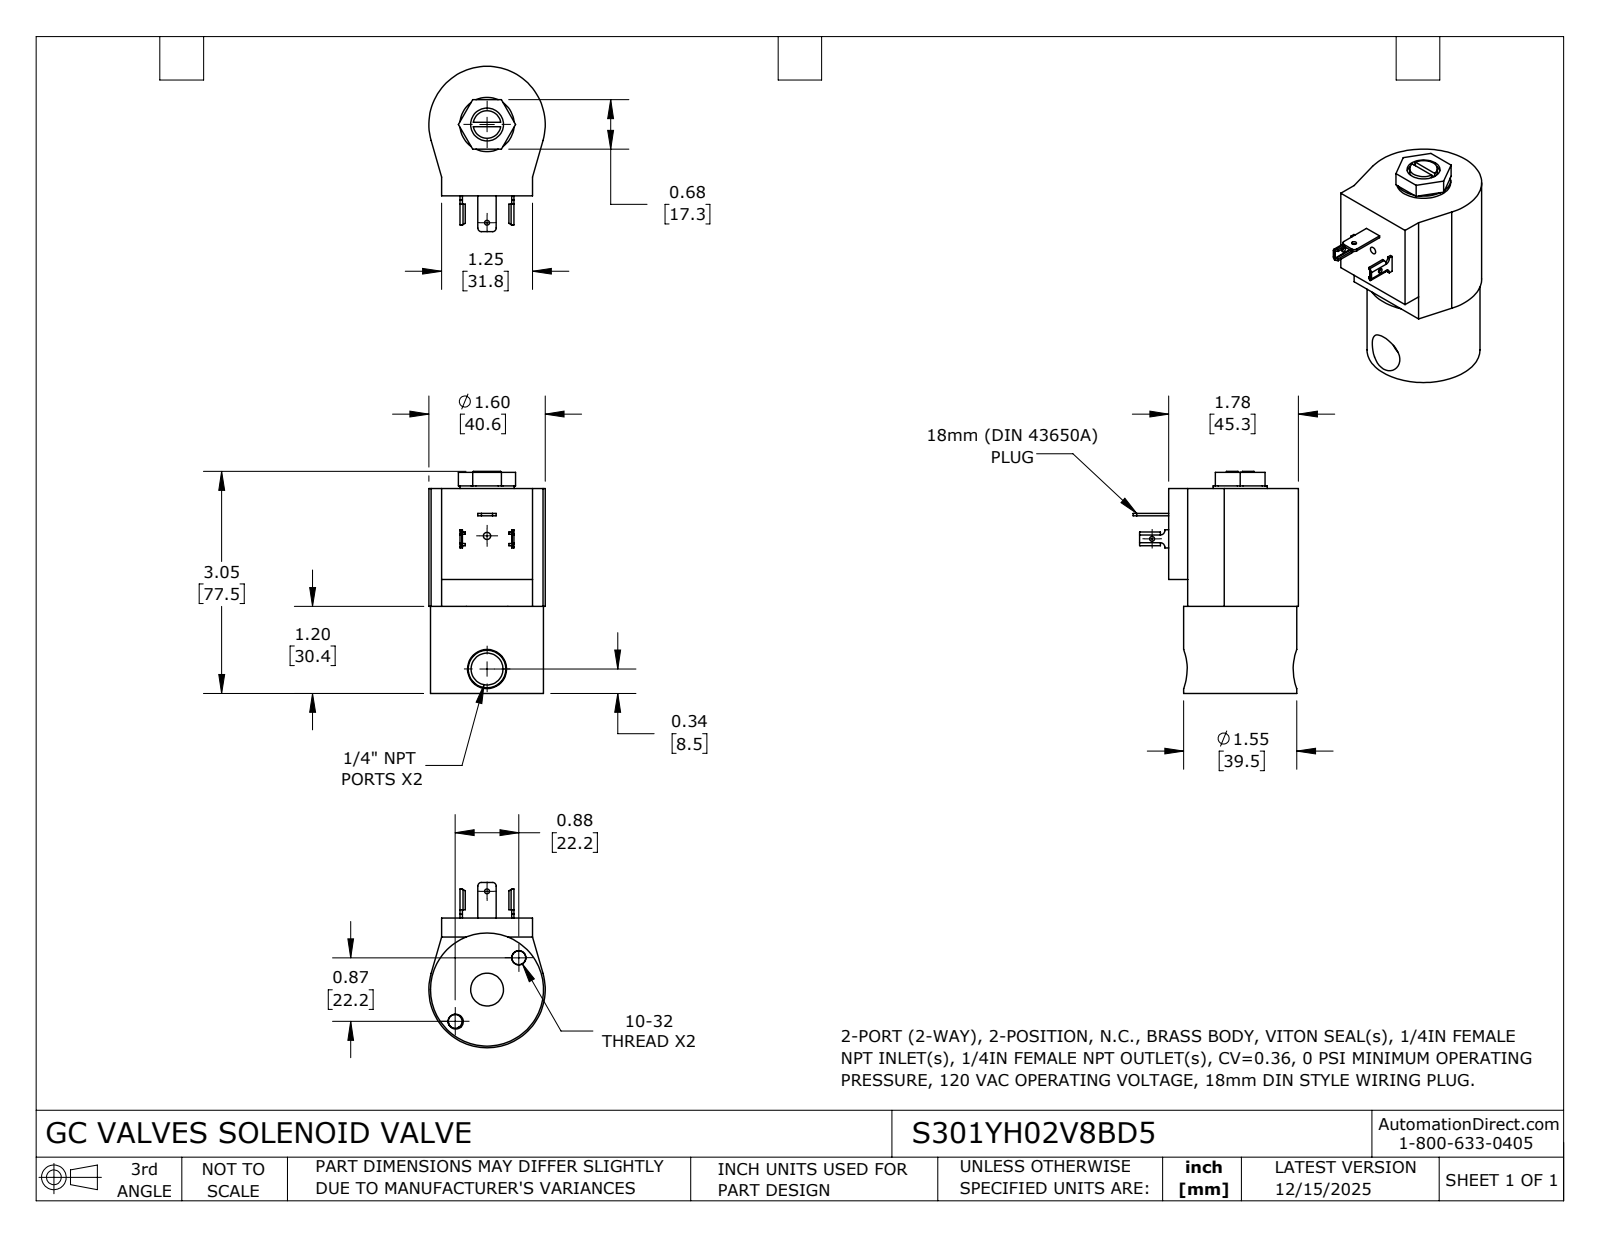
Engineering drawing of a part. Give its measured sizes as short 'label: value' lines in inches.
name: S301YH02V8BD5
written by: SolidWorks 2024 (CONFIG_CONTROL_DESIGN)
unit: in
bodies: 2 solids, 171 faces (78 planar, 71 cylindrical, 22 other)
size: 3.061 × 2.273 × 1.6
volume: 5.834 in³; area: 27.56 in²
holes: 2× ⌀0.19, 1× ⌀0.066, 1× ⌀0.067, 1× ⌀0.1, 1× ⌀0.438, 1× ⌀0.451
bosses: 1× ⌀1.553, 1× ⌀0.746, 1× ⌀0.38
rounds: 4× R0.006, 4× R0.041, 2× R0.05, 2× R0.06, 1× R0.8
face distances: 1.62, 1.195, 2.815, 0.26, 1.565, 0.37, 1.25, 1.25, 3.038, 1.843
hole spacings: 0.618, 0.619, 1.012, 1.237, 1.35, 1.83, 1.84
